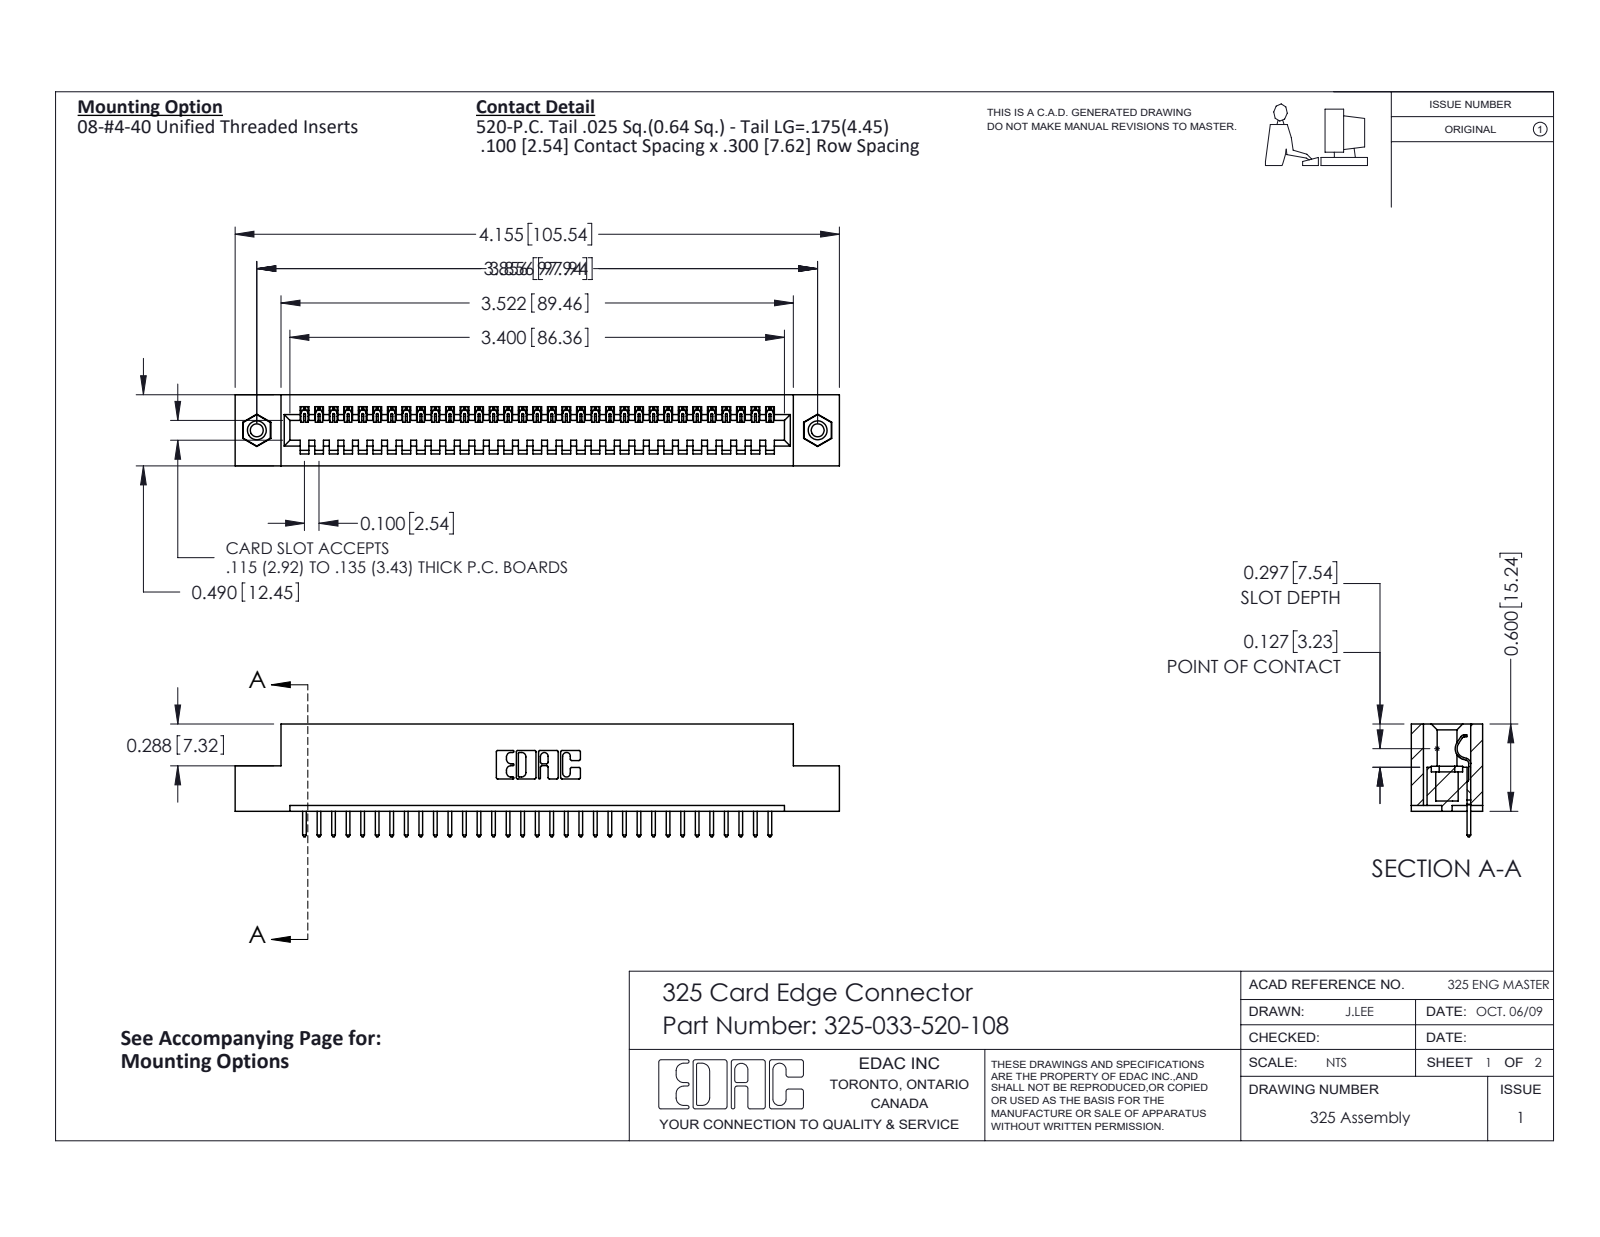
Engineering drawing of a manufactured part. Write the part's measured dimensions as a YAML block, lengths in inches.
part_name: "325-292-001_325-293-120; 345-250-001_345-250-003-102; 325-033-520-108; 325 Part_TI"
step_written_by: "SolidWorks 2016 (CONFIG_CONTROL_DESIGN)"
units: inches
bodies: {solids: 36, faces: 2088, planar: 1488, cylindrical: 584, other: 16}
overall_size: [4.155, 0.775, 0.49]
volume: 0.808
surface_area: 21.66
round_holes:
  - {diameter: 0.089, count: 2}
  - {diameter: 0.125, count: 2}
  - {diameter: 0.16, count: 2}
round_bosses_or_shafts:
  - {diameter: 0.155, count: 2}
partial_cylinders:
  - {radius: 0.006, count: 66}
  - {radius: 0.01, count: 66}
  - {radius: 0.01, count: 22}
  - {radius: 0.007, count: 6}
  - {radius: 0.031, count: 6}
  - {radius: 0.026, count: 3}
  - {radius: 0.014, count: 1}
  - {radius: 0.022, count: 1}
face_to_face_distances: [0.083, 0.407, 0.49, 0.3, 0.107, 0.383, 0.025, 0.325, 0.56, 0.04]
hole_center_spacings: [3.856]
